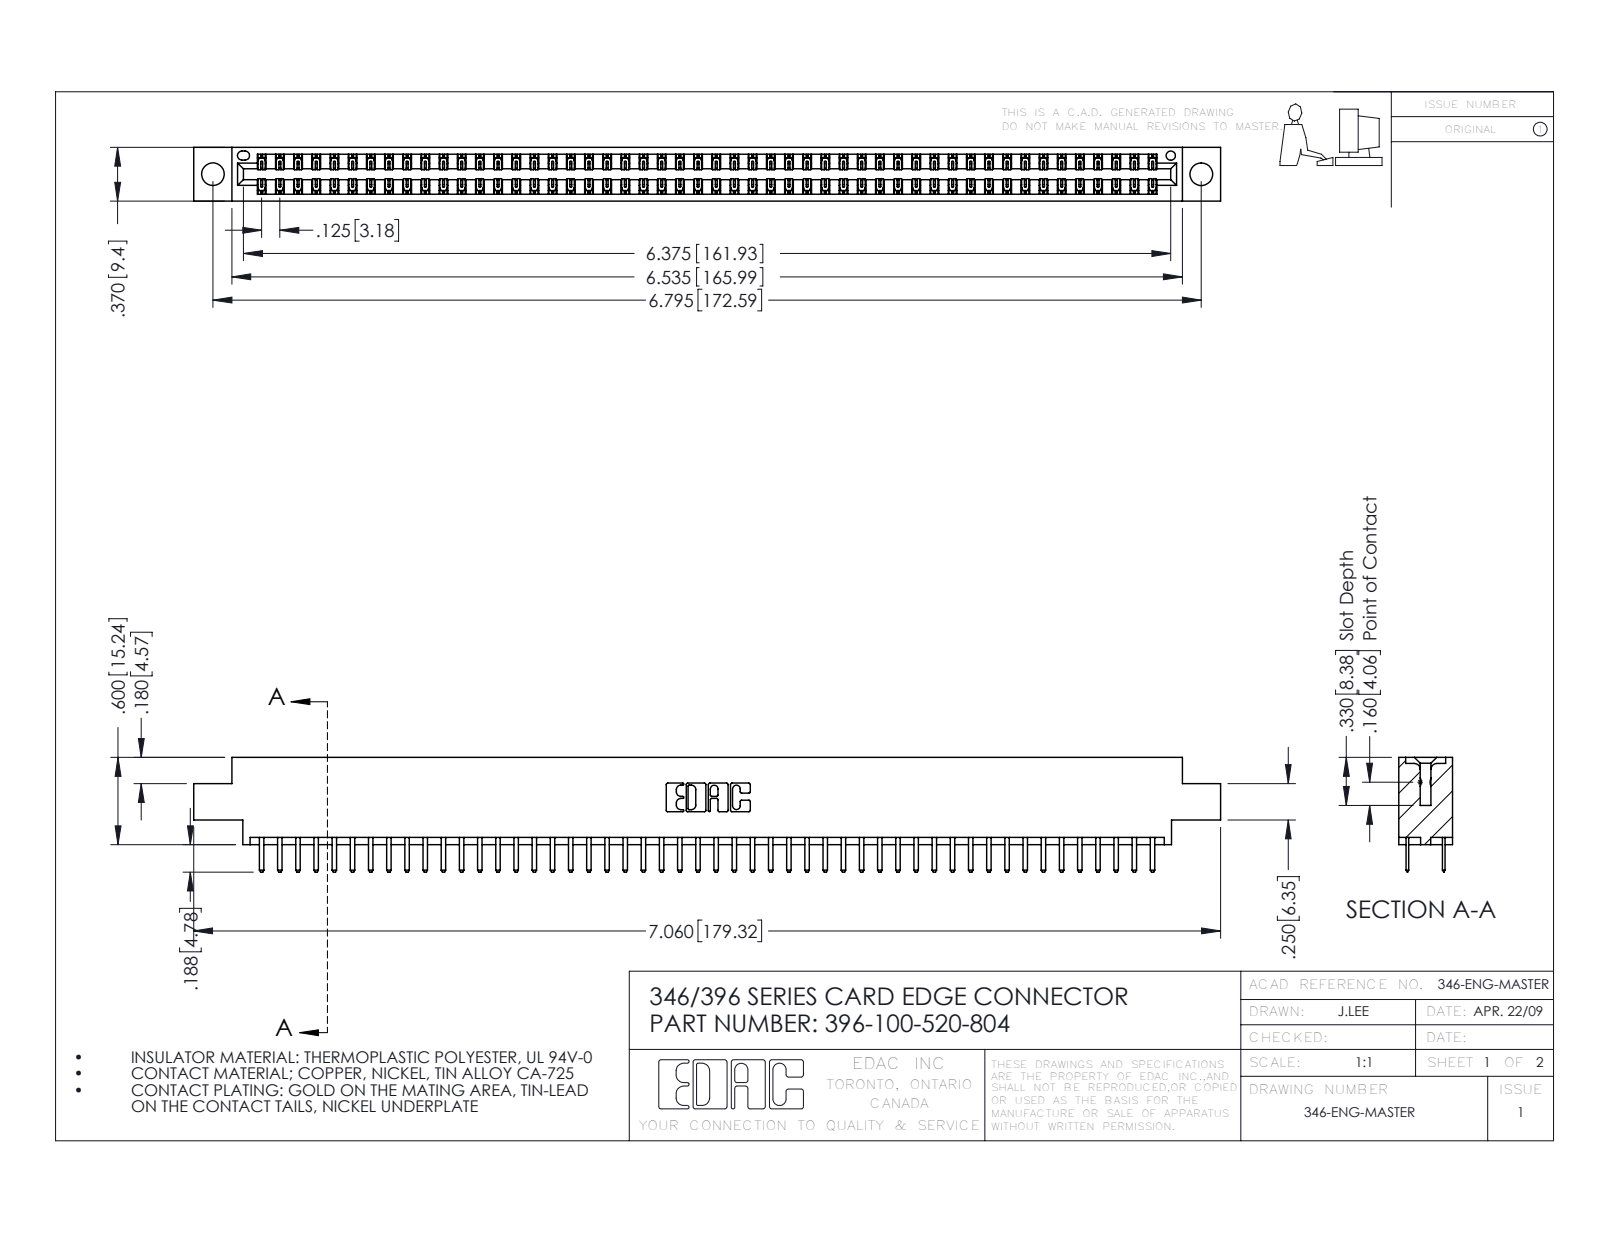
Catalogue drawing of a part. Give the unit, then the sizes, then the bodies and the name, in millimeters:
Units: millimetres
Overall size (bounding box): 179.3 × 20 × 9.4
Round holes (diameter × count): ⌀4 ×2, ⌀1.6 ×1
Partial cylindrical surfaces — rounded edges, fillets, slot ends (radius × count): R0.2 ×150, R0.3 ×104, R0.3 ×22, R0.2 ×6, R0.8 ×6, R0.7 ×3, R0.4 ×2, R0.6 ×2
Main face-to-face distances: 1.2, 8.2, 6.4, 9.4, 7, 1.8, 7.6, 0.6, 3.8, 5.6
Hole centre spacings: 6.2, 167.3, 172.6
Volume: 17 260 mm³ · Surface area: 23 740 mm²
Bodies: 101 solids, 5726 faces (3780 planar, 1946 cylindrical, 0 other)
Part name (STEP PRODUCT): 346 Part_0.170 Offset - 0.156 Dia-TH; 345-292-001_345-293-120; 396-100-520-804
STEP written by: SolidWorks 2016 (CONFIG_CONTROL_DESIGN)
